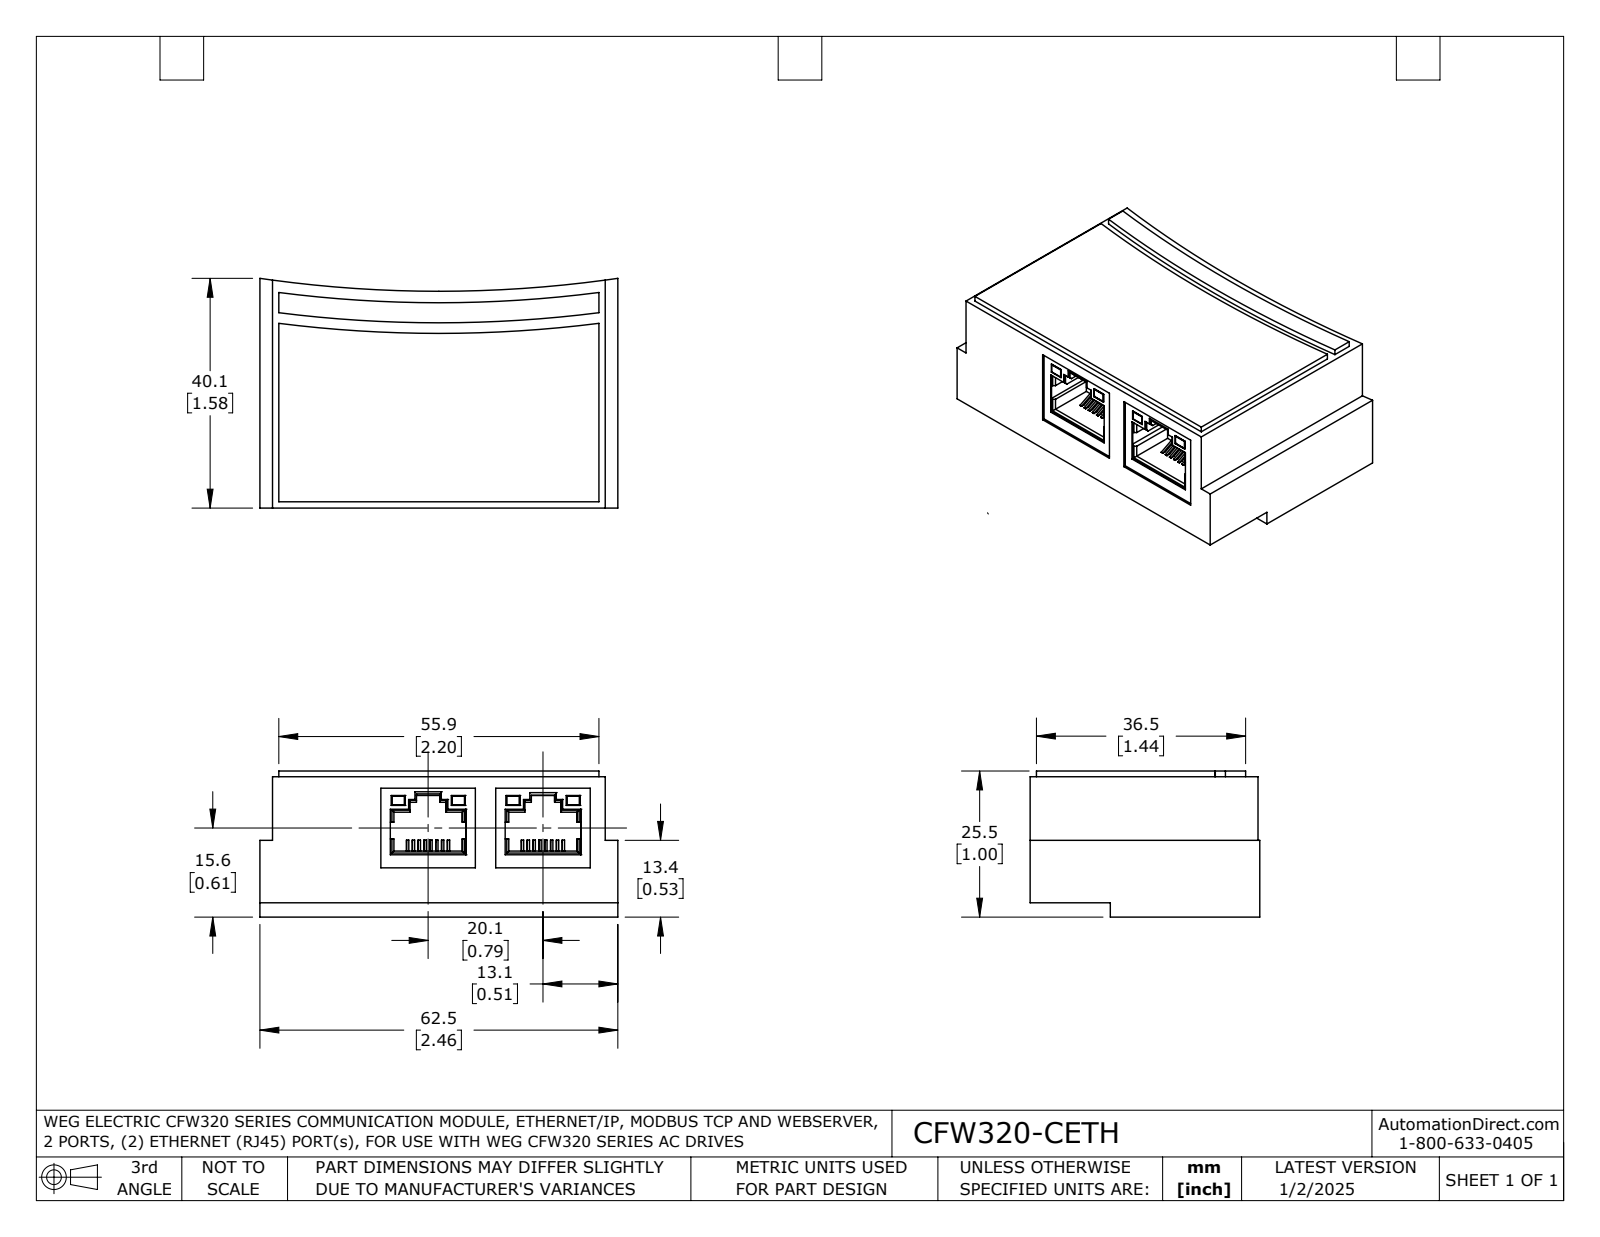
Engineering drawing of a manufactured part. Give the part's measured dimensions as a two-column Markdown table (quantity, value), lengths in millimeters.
| quantity | value |
| --- | --- |
| part name | CFW320 CETH |
| STEP written by | SolidWorks 2021 (AUTOMOTIVE_DESIGN) |
| units | millimeters |
| bodies | 1 solid, 276 faces (255 planar, 21 cylindrical, 0 other) |
| overall size | 62.5 × 40.1 × 25.5 |
| volume | 54 960 mm³ |
| surface area | 10 910 mm² |
| partial cylindrical surfaces (radius × count) | 0.5 × 1, 217 × 1, 219 × 1, 222.5 × 1, 223 × 1 |
| main face-to-face distances | 25.5, 2.2, 60.3, 2.5, 23, 62.5, 58.1, 24.5, 22, 1 |
